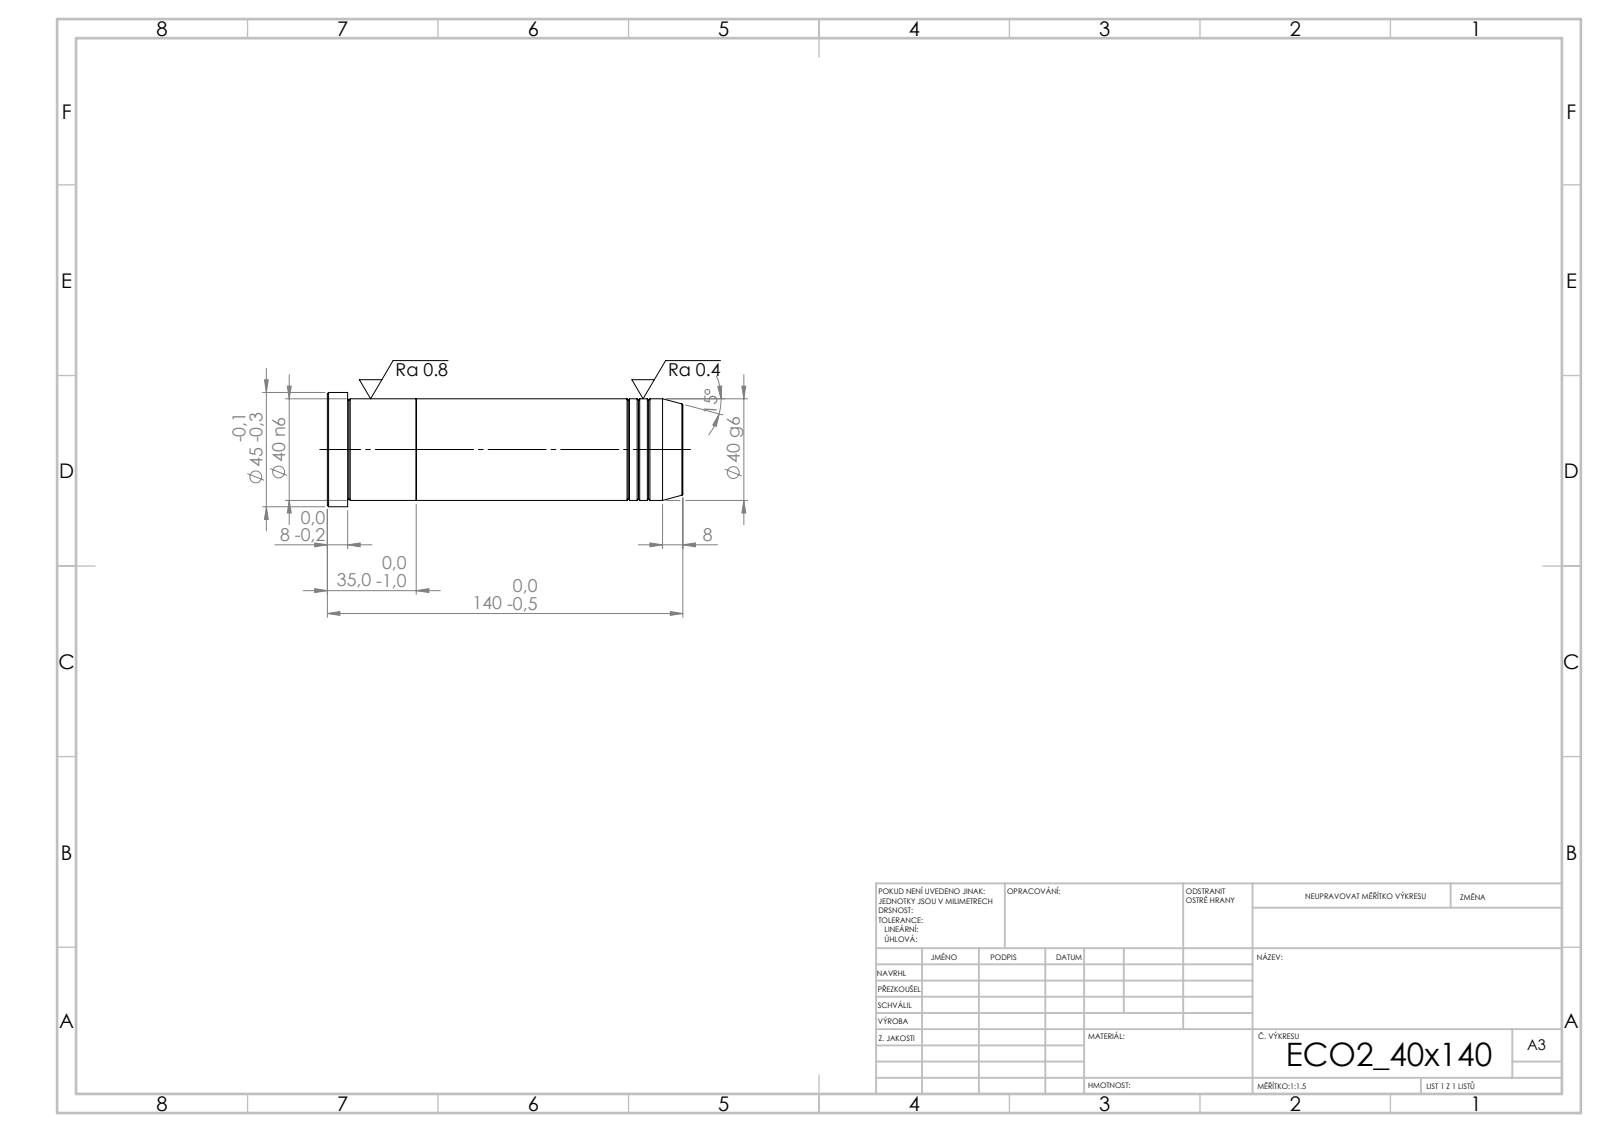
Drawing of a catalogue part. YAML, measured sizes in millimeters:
step_written_by: "SolidWorks 2019 (CONFIG_CONTROL_DESIGN)"
units: millimeters
bodies: {solids: 2, faces: 39, planar: 5, cylindrical: 12, other: 22}
overall_size: [140, 45, 45]
volume: 177345
surface_area: 23357
round_bosses_or_shafts:
  - {diameter: 45, count: 1}
  - {diameter: 40, count: 1}
face_to_face_distances: [35, 105, 140, 132, 27, 8]
